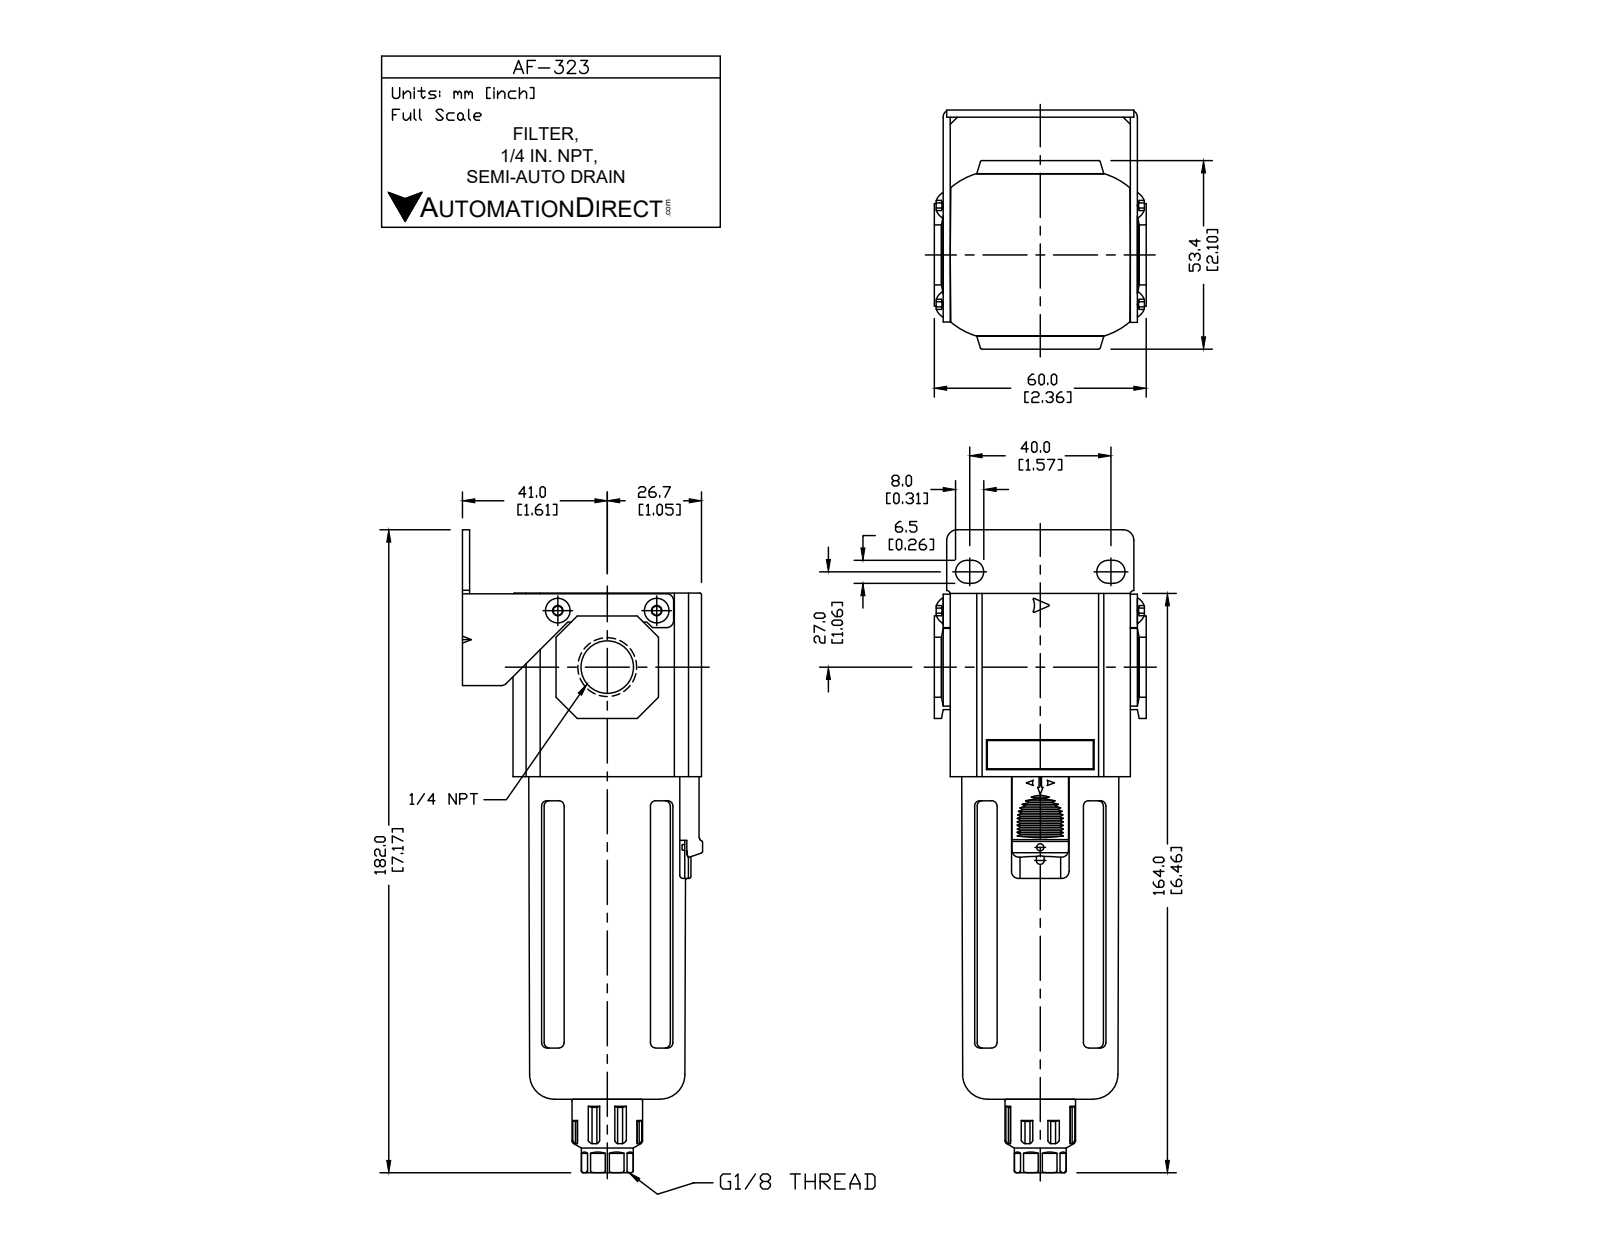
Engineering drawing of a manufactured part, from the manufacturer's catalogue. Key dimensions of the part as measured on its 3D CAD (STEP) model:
Part name (STEP PRODUCT): AF-323
STEP written by: SolidWorks 2015 (CONFIG_CONTROL_DESIGN)
Units: millimetres
Bodies: 9 solids, 390 faces (246 planar, 94 cylindrical, 50 other)
Overall size (bounding box): 182.3 × 67.7 × 60
Volume: 206 183 mm³ · Surface area: 60 574 mm²
Round holes (diameter × count): ⌀3.4 ×2, ⌀8.57 ×1, ⌀11.13 ×1, ⌀35.99 ×1, ⌀44.8 ×1
Round bosses / shafts (diameter × count): ⌀44.47 ×1, ⌀26 ×1, ⌀22.24 ×1, ⌀14.82 ×1
Partial cylindrical surfaces — rounded edges, fillets, slot ends (radius × count): R1 ×18, R2 ×8, R9.5 ×8, R0.5 ×6, R0.3 ×4, R3.25 ×4, R20 ×4, R0.2 ×3
Main face-to-face distances: 2, 51, 2.5, 53, 12.3, 67.7, 65.7, 14.3, 53.4, 55.5
Hole centre spacings: 21.06, 21.46, 28
